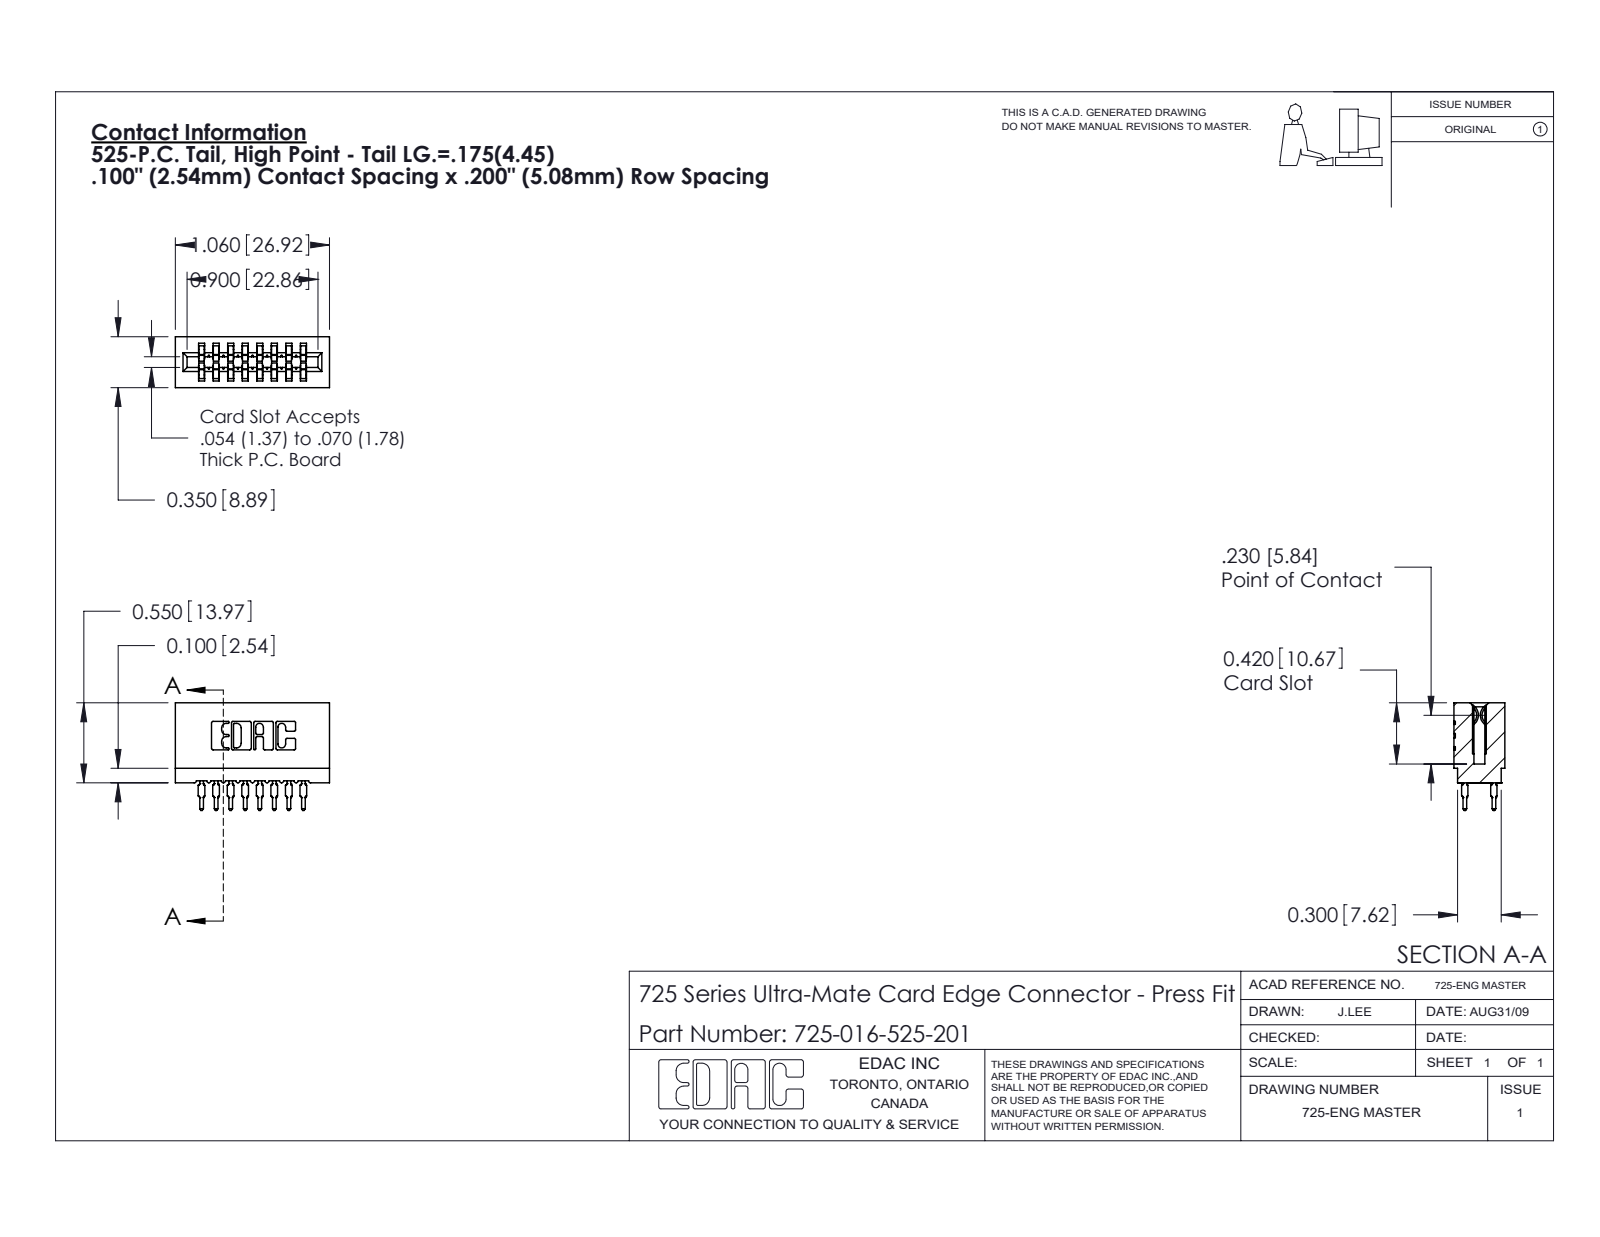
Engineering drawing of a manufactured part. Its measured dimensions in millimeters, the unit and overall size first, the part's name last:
Units: millimetres
Overall size (bounding box): 26.9 × 18.8 × 8.9
Partial cylindrical surfaces — rounded edges, fillets, slot ends (radius × count): R0.5 ×32, R0.3 ×22, R0.4 ×16, R0.1 ×8, R0.3 ×8, R0.2 ×6, R0.8 ×6, R0.7 ×3
Main face-to-face distances: 2.5, 5.1, 7.6, 10.2, 1.1, 3.6, 1.5, 12.7, 6.1, 4
Volume: 2 290 mm³ · Surface area: 4 125 mm²
Bodies: 17 solids, 1527 faces (791 planar, 320 cylindrical, 416 other)
Part name (STEP PRODUCT): 725 Part_Insulator Option - 01; 745-292-001_525; 725-016-525-201
STEP written by: SolidWorks 2020 (CONFIG_CONTROL_DESIGN)
